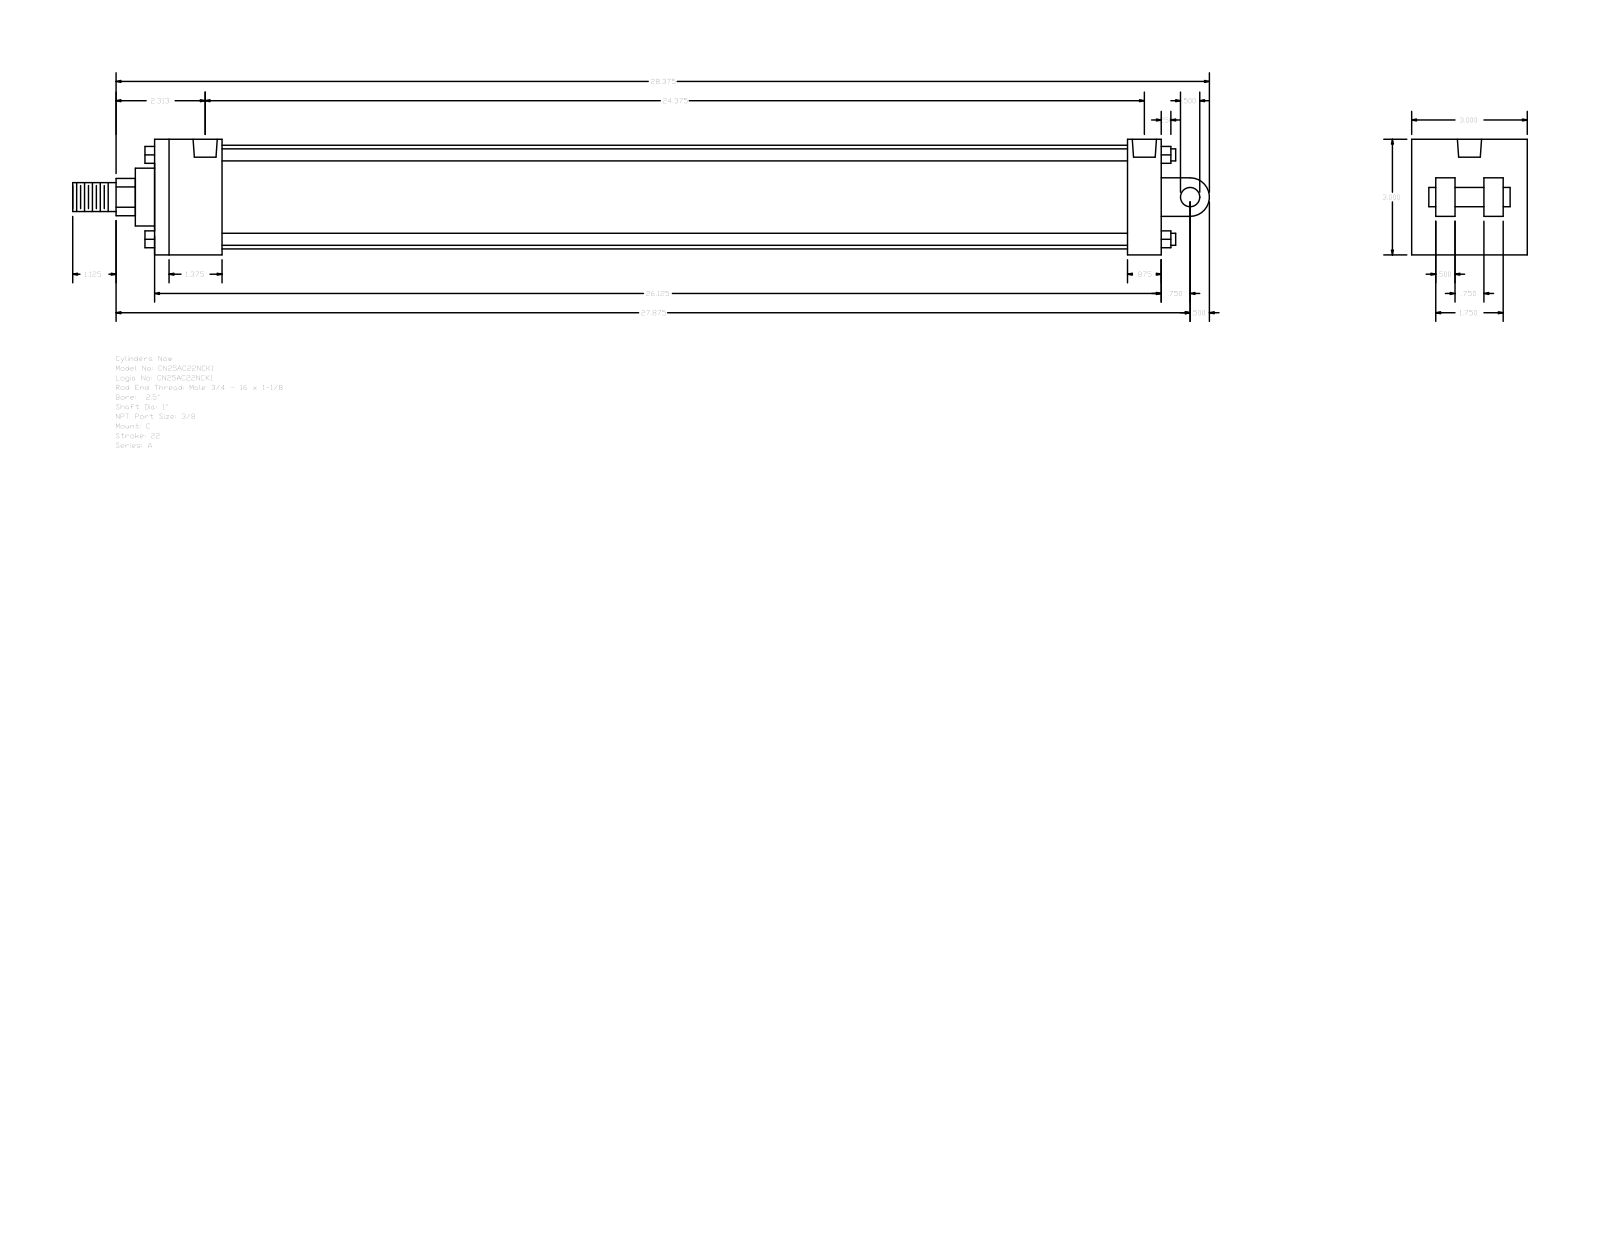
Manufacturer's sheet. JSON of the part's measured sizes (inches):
{"part_name": "A_C__0250_1", "step_written_by": "GSSL Pune (CONFIG_CONTROL_DESIGN)", "units": "inches", "bodies": {"solids": 0, "faces": 135, "planar": 102, "cylindrical": 33, "other": 0}, "overall_size": [29.5, 3, 3], "round_holes": [[0.219, 4], [0.627, 2]], "round_bosses_or_shafts": [[0.313, 4], [2.69, 1], [1.5, 1], [1, 1], [0.75, 1], [0.5, 1]], "partial_cylinders_radius": [[0.484, 1], [0.5, 1]], "face_to_face_distances": [3, 26.125, 0.5, 1.75, 25.25, 23.5, 24.375, 0.875, 0.625, 1], "hole_center_spacings": [0.094, 24.469, 24.562, 24.375]}
